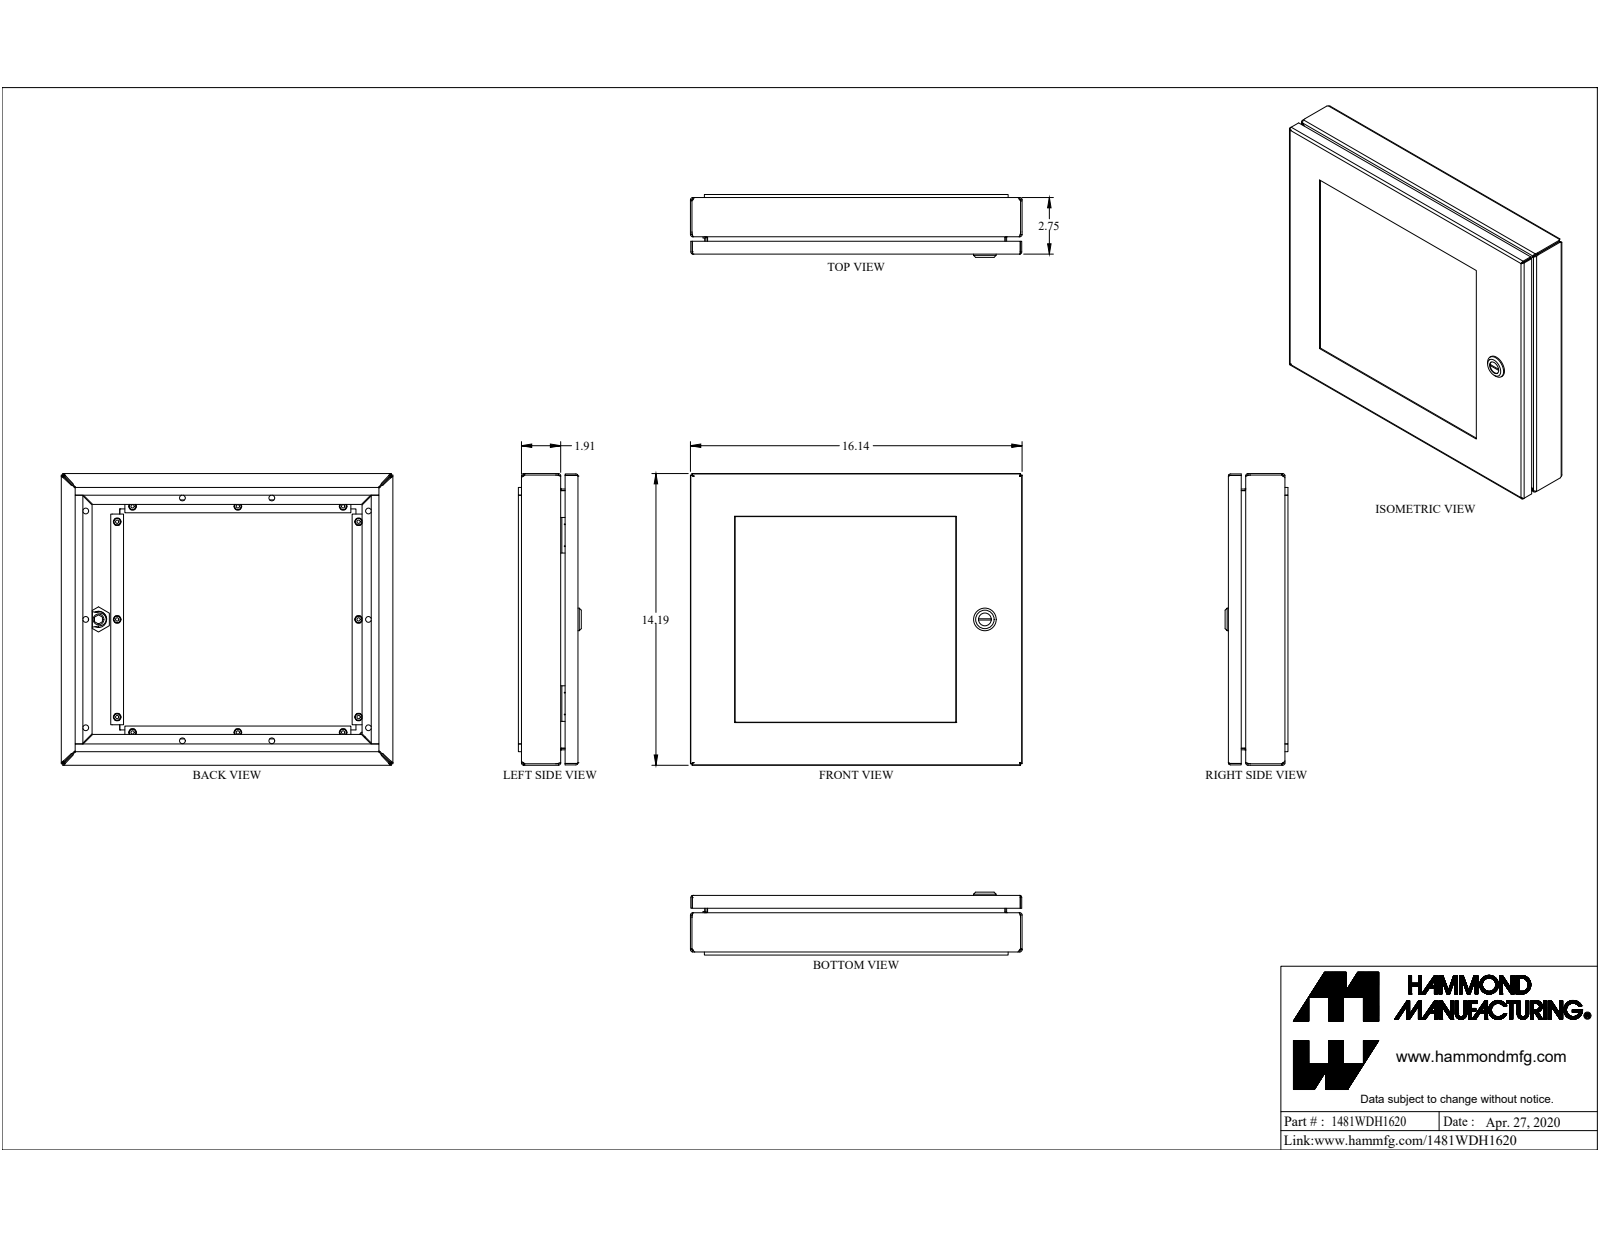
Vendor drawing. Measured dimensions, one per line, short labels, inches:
name: 1481WDH1620
written by: SolidWorks 2019 (CONFIG_CONTROL_DESIGN)
unit: in
bodies: 56 solids, 1031 faces (623 planar, 238 cylindrical, 170 other)
size: 16.14 × 14.19 × 3.061
volume: 74.92 in³; area: 1 464 in²
holes: 12× ⌀0.13, 12× ⌀0.25, 10× ⌀0.281, 1× ⌀0.172, 1× ⌀0.232, 1× ⌀0.24, 1× ⌀0.242, 1× ⌀0.625, 1× ⌀0.785
bosses: 13× ⌀0.226, 12× ⌀0.368, 12× ⌀0.164, 1× ⌀1.1, 1× ⌀0.525, 1× ⌀0.455, 1× ⌀0.398, 1× ⌀0.356
rounds: 28× R0.036, 28× R0.108, 12× R0.382, 8× R19.003, 4× R0.006, 4× R0.016, 4× R0.062, 4× R0.088
face distances: 0.072, 0.25, 0.215, 0.287, 2.579, 0.037, 0.035, 2.614, 0.843, 1.736
hole spacings: 15.036, 11.75, 4.75, 11.026, 1.061, 1.061, 4.38, 4.75
